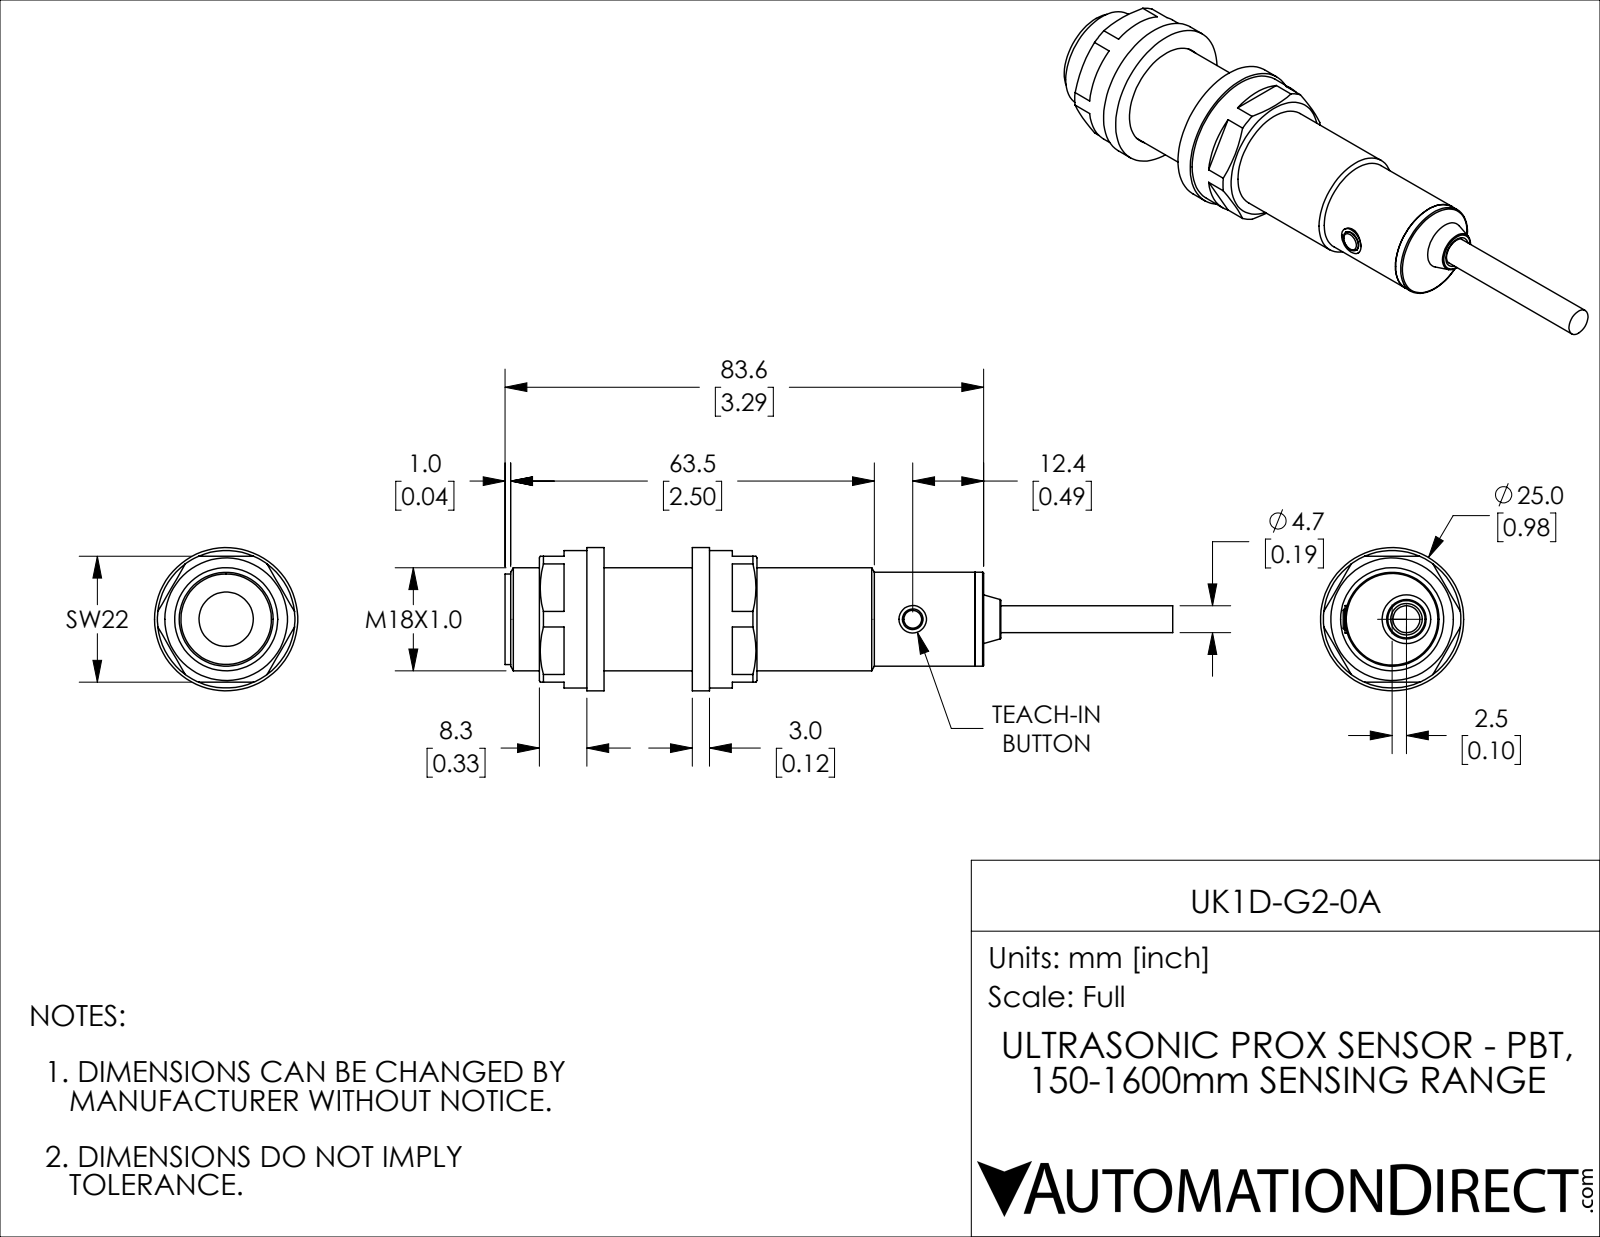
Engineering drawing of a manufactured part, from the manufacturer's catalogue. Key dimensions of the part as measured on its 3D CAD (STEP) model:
Part name (STEP PRODUCT): UK1D-G2-0A
STEP written by: SolidWorks 2018 (AUTOMOTIVE_DESIGN)
Units: millimetres
Bodies: 10 solids, 107 faces (49 planar, 40 cylindrical, 18 other)
Overall size (bounding box): 116.6 × 25 × 25
Volume: 25 220 mm³ · Surface area: 11 419 mm²
Round holes (diameter × count): ⌀4.7 ×2, ⌀3.6 ×1, ⌀9.5 ×1, ⌀18 ×1, ⌀18.2 ×1
Round bosses / shafts (diameter × count): ⌀25 ×1, ⌀24 ×1, ⌀16.4 ×1, ⌀15.8 ×1, ⌀5.4 ×1, ⌀4.8 ×1
Main face-to-face distances: 3, 18.4, 21.4, 67.8, 46.4, 13.3, 34.7, 81.1, 16.3, 64.8
Hole centre spacings: 2.5
